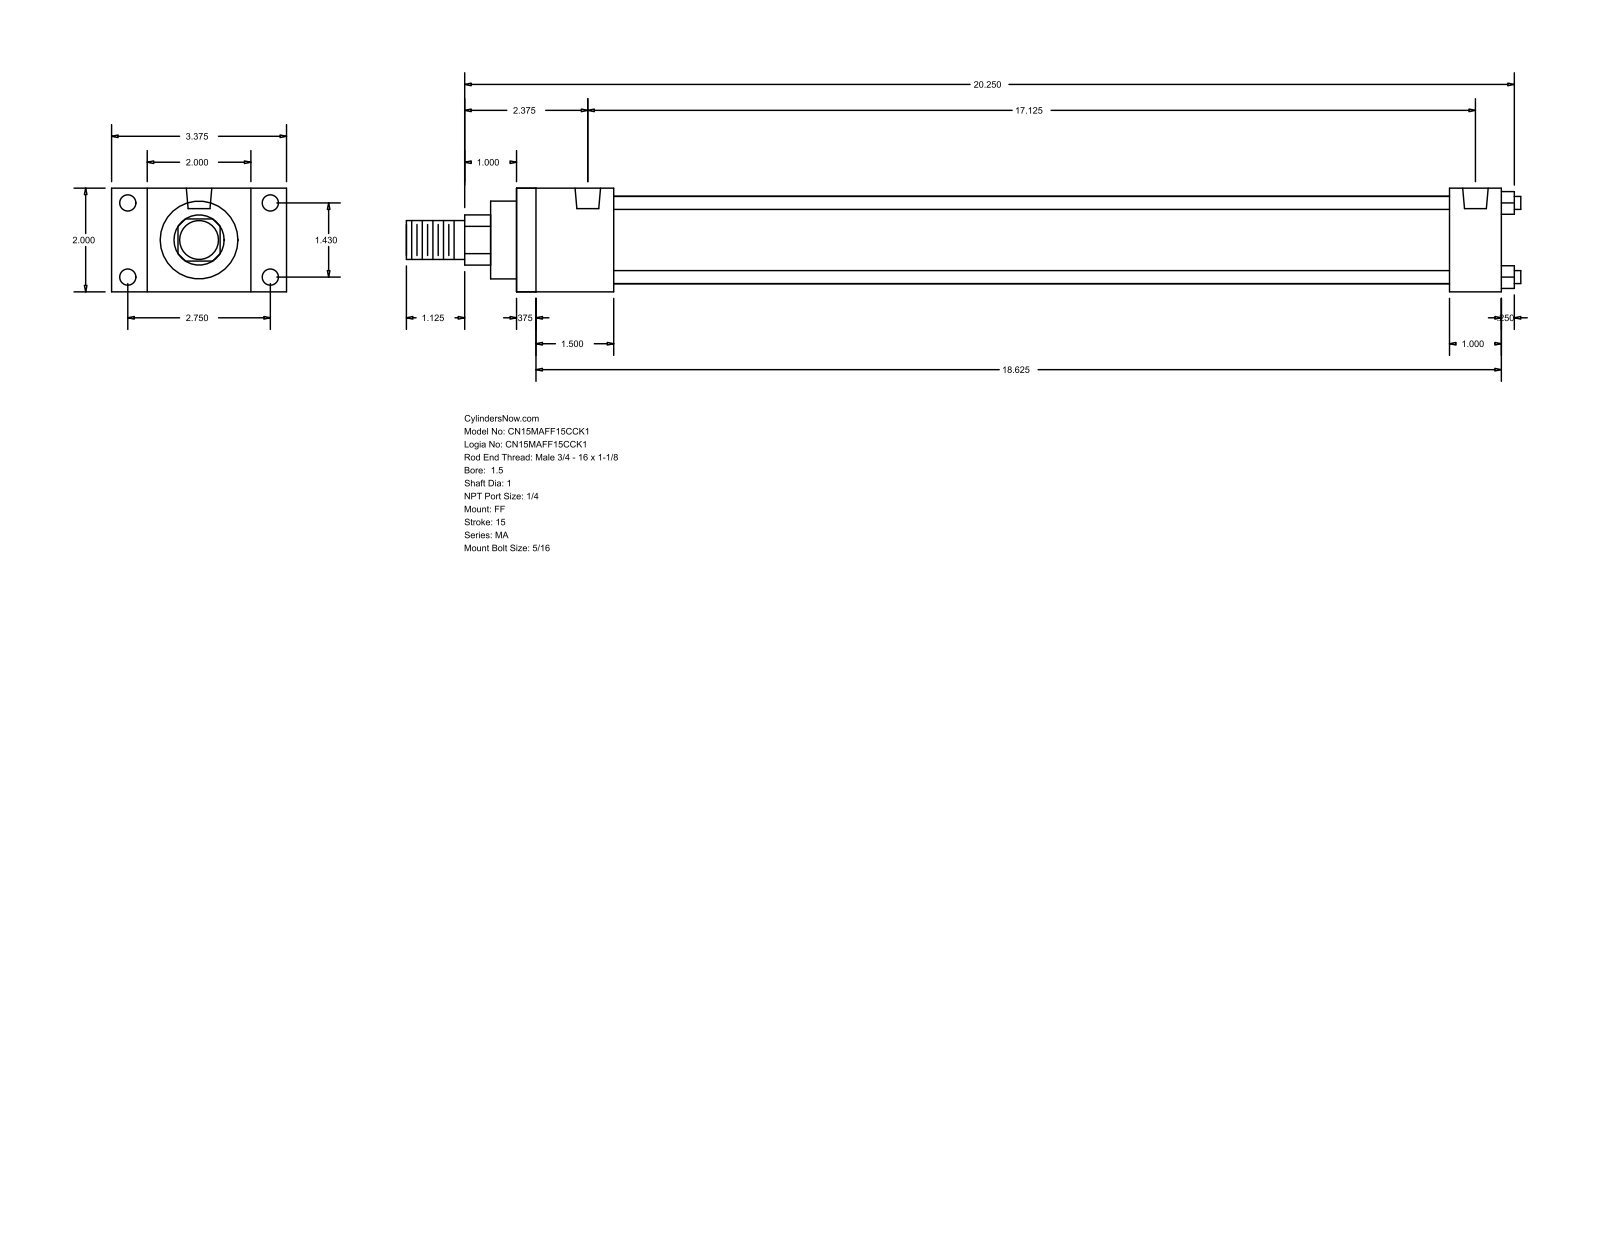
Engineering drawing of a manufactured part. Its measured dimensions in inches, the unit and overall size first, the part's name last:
Units: inches
Overall size (bounding box): 21.5 × 3.375 × 2
Round holes (diameter × count): ⌀0.313 ×8, ⌀0.492 ×2
Round bosses / shafts (diameter × count): ⌀0.25 ×4, ⌀1.69 ×1, ⌀1.5 ×1, ⌀1 ×1, ⌀0.75 ×1
Partial cylindrical surfaces — rounded edges, fillets, slot ends (radius × count): R0.484 ×1
Main face-to-face distances: 2, 19, 0.375, 18.625, 1, 1.875, 18, 1.5, 17.625, 16.125
Hole centre spacings: 1.43, 2.75, 3.099, 17.125
Bodies: 0 solids, 92 faces (64 planar, 28 cylindrical, 0 other)
Part name (STEP PRODUCT): MA_FF__0150_1
STEP written by: GSSL Pune (CONFIG_CONTROL_DESIGN)
